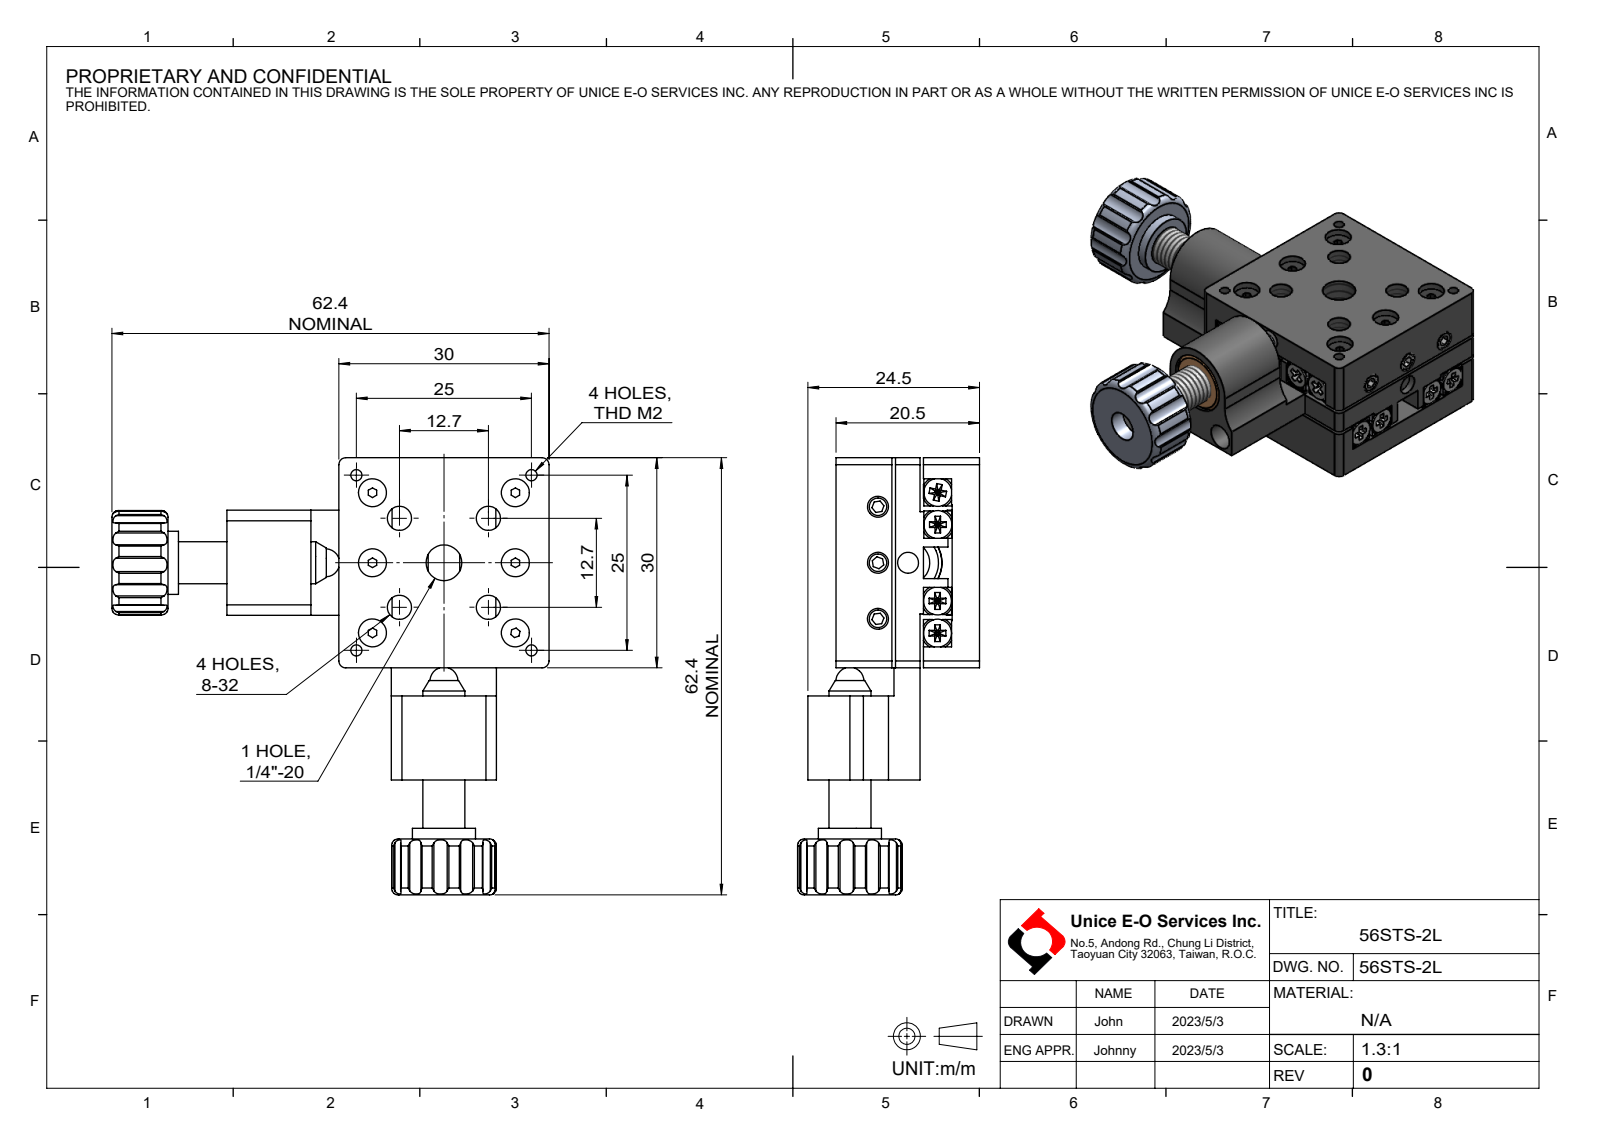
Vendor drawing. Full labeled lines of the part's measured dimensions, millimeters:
Part name (STEP PRODUCT): 56STS-2L
STEP written by: SolidWorks 2022 (CONFIG_CONTROL_DESIGN)
Units: millimetres
Bodies: 0 solids, 888 faces (545 planar, 261 cylindrical, 82 other)
Overall size (bounding box): 62.4 × 62.4 × 25.97
Round holes (diameter × count): ⌀4 ×10, ⌀1.6 ×4, ⌀3.3 ×4, ⌀3.45 ×4, ⌀4.2 ×3, ⌀2.5 ×2, ⌀4.7 ×2, ⌀9.5 ×2, ⌀3 ×1, ⌀5 ×1, ⌀5.11 ×1
Round bosses / shafts (diameter × count): ⌀4 ×10, ⌀2 ×4, ⌀9 ×2, ⌀6 ×2
Partial cylindrical surfaces — rounded edges, fillets, slot ends (radius × count): R0.3 ×48, R1.5 ×24, R2 ×6, R1 ×4, R5 ×4, R6 ×2, R7.5 ×2
Main face-to-face distances: 4, 8, 8.5, 3.9, 4.5, 12.5, 4.6, 12, 0.5, 15.5
Hole centre spacings: 8.84, 10, 12.6, 19.76, 19.83, 10.2, 3.4, 5.31
